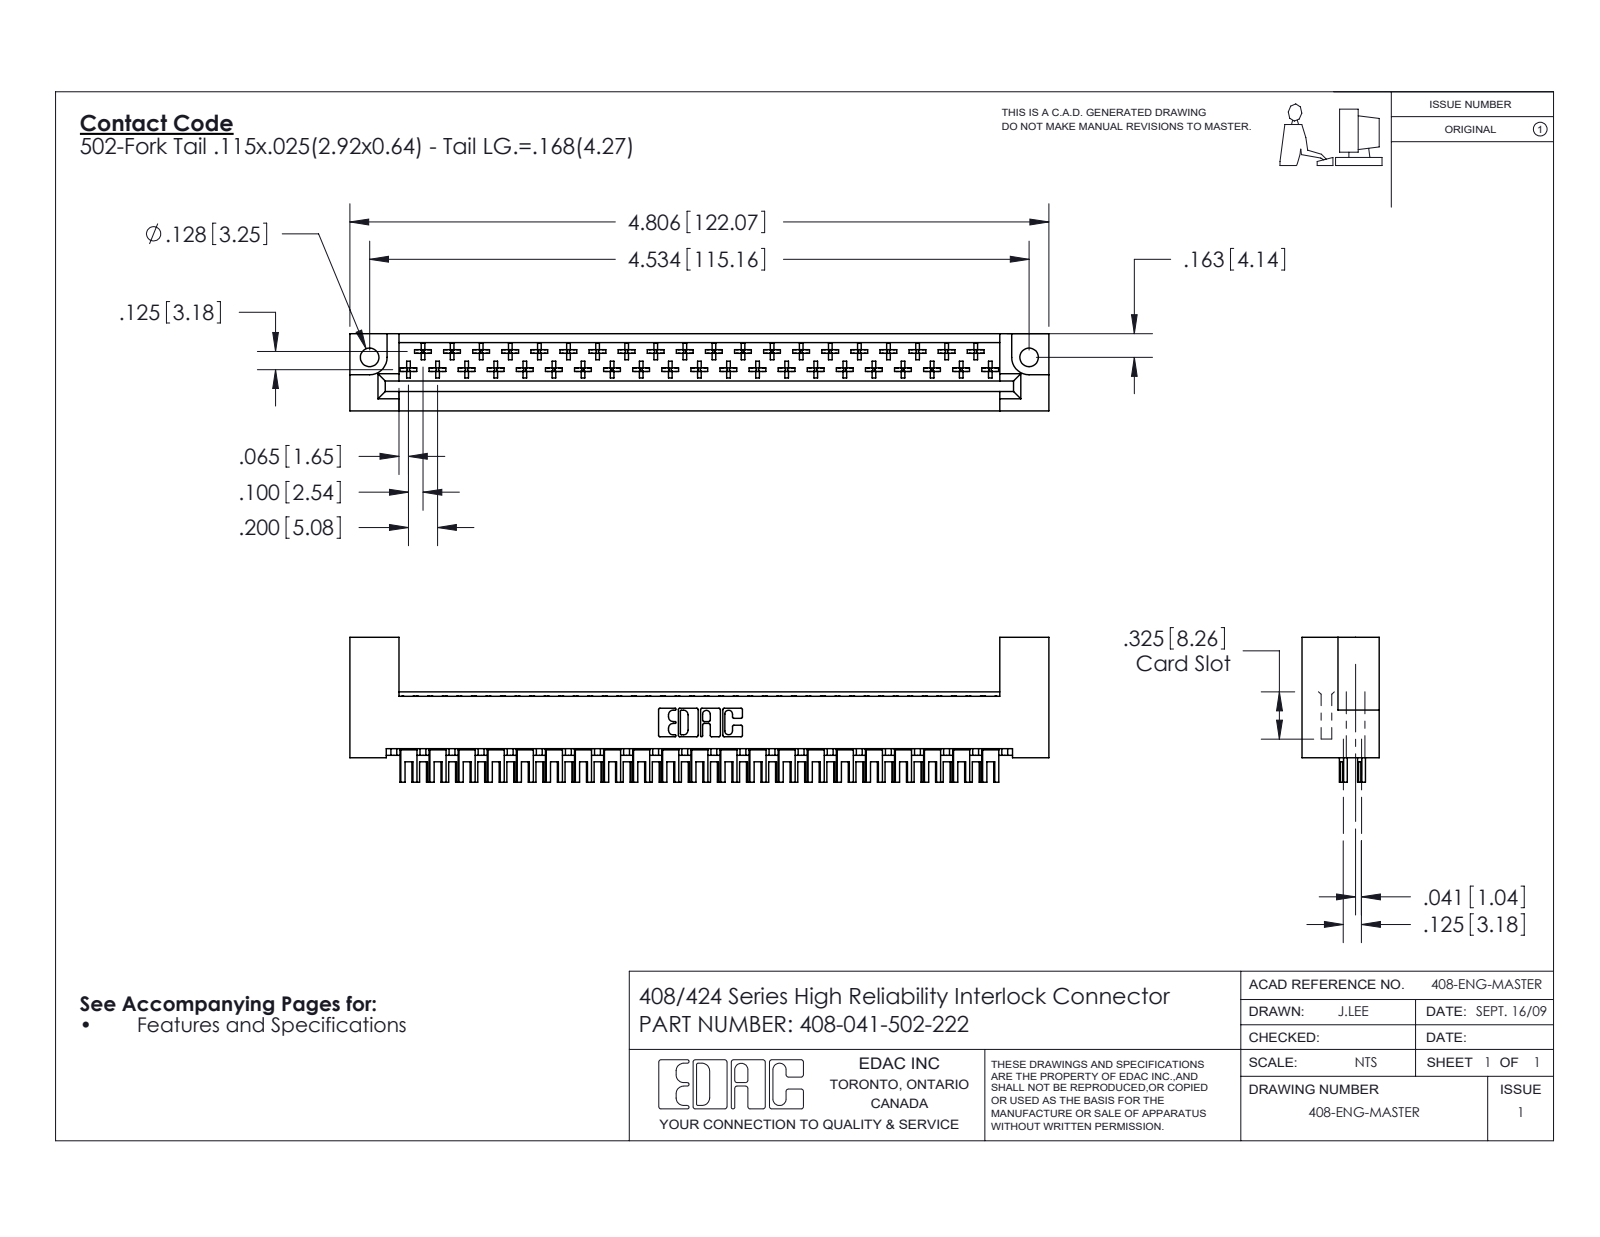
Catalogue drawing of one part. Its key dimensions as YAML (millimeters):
part_name: "408-047-502-222; 408-290-001_408-290-102; 408 Part_041 - 2"
step_written_by: "SolidWorks 2016 (CONFIG_CONTROL_DESIGN)"
units: millimeters
bodies: {solids: 42, faces: 2312, planar: 1770, cylindrical: 378, other: 164}
overall_size: [122.1, 25.3, 13.5]
volume: 15100
surface_area: 18030
round_holes:
  - {diameter: 3.3, count: 2}
partial_cylinders:
  - {radius: 0.3, count: 246}
  - {radius: 0.5, count: 43}
  - {radius: 0.3, count: 22}
  - {radius: 0.2, count: 6}
  - {radius: 0.8, count: 6}
  - {radius: 0.7, count: 3}
  - {radius: 3, count: 2}
face_to_face_distances: [13.5, 3.2, 2.5, 0.6, 0.6, 9.2, 6, 6.6, 5.5, 6.9]
hole_center_spacings: [115.2]
